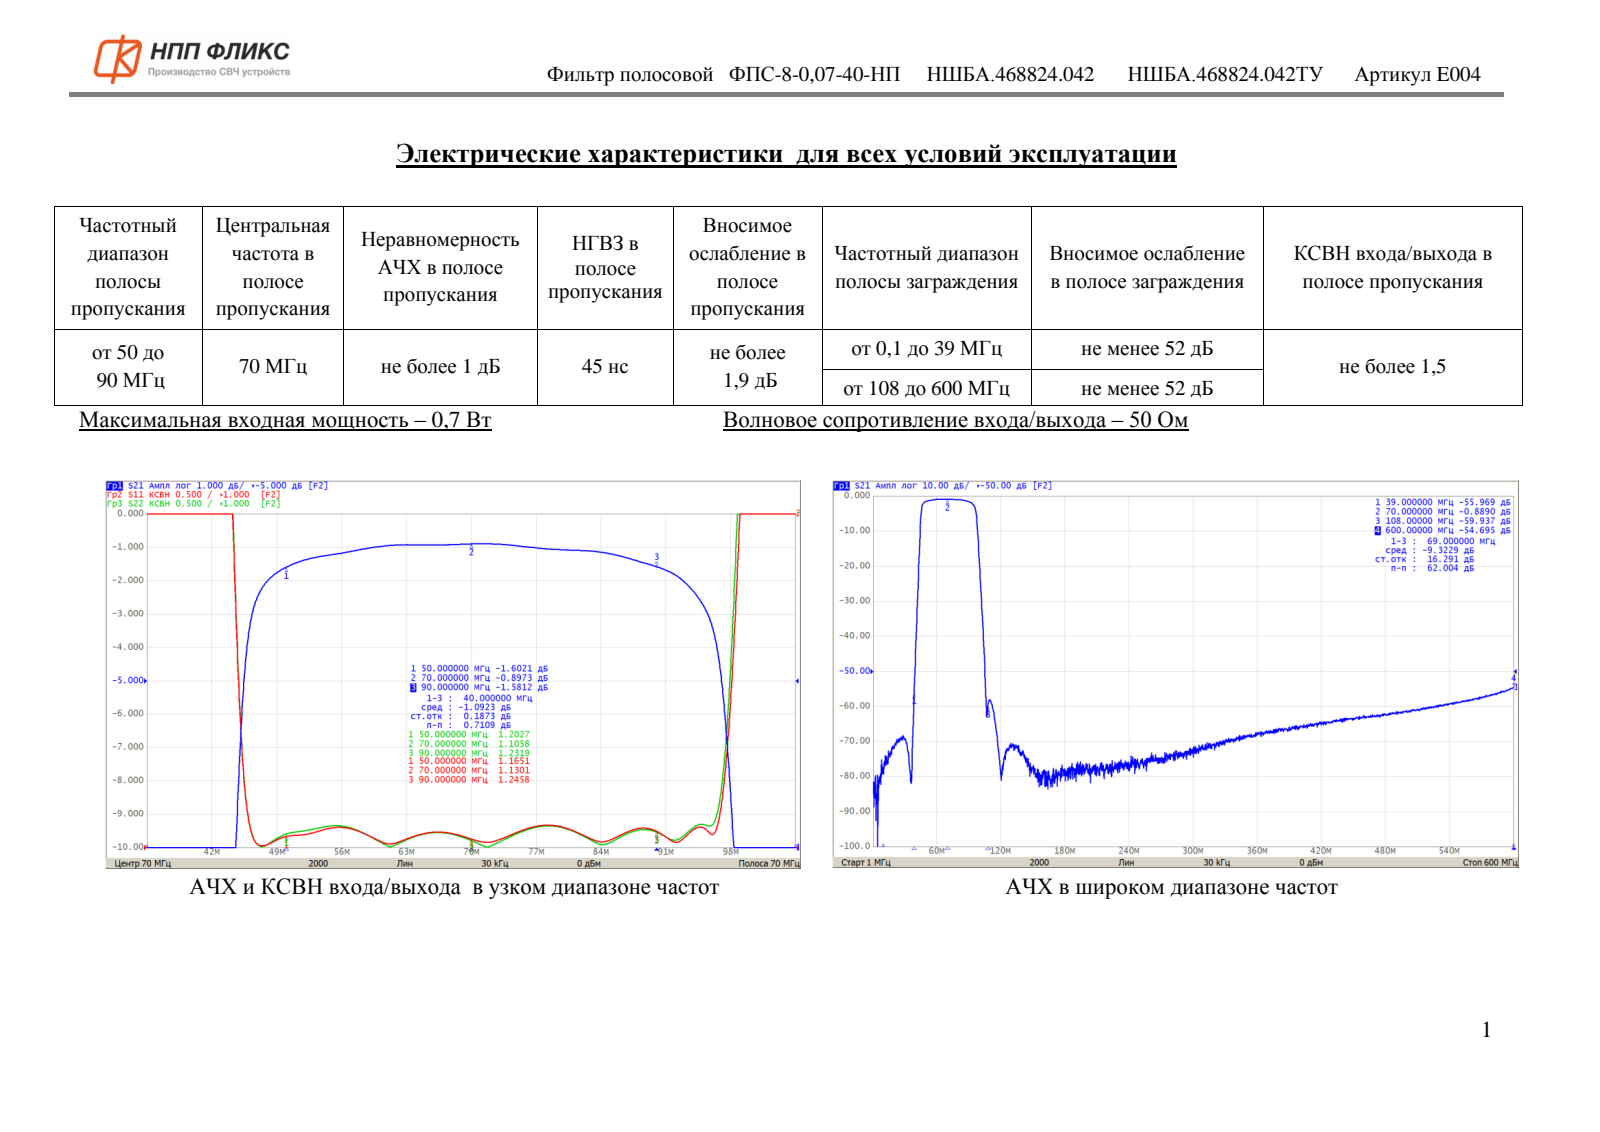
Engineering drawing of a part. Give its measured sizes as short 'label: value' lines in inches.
name: НШБА.468824.042_Фильтр ФПС-8-0,07-40-НП
written by: ASCON Math Kernel (CONFIG_CONTROL_DESIGN)
unit: in
bodies: 1 solid, 1276 faces (1019 planar, 130 cylindrical, 127 other)
size: 1.181 × 0.787 × 0.248
volume: 0.017 in³; area: 6.202 in²
holes: 7× ⌀0.039, 4× ⌀0.055
bosses: 5× ⌀0.063
rounds: 33× R0.024, 32× R0.02, 11× R0.028, 5× R0.012, 4× R0.008, 4× R0.014, 4× R0.031, 1× R0.035
face distances: 0.016, 0.039, 0.701, 0.236, 0.248, 0.197, 0.209, 0.028, 1.094, 0.685
hole spacings: 0.24, 0.331, 0.488, 0.572, 0.616, 0.685, 0.841, 0.326
